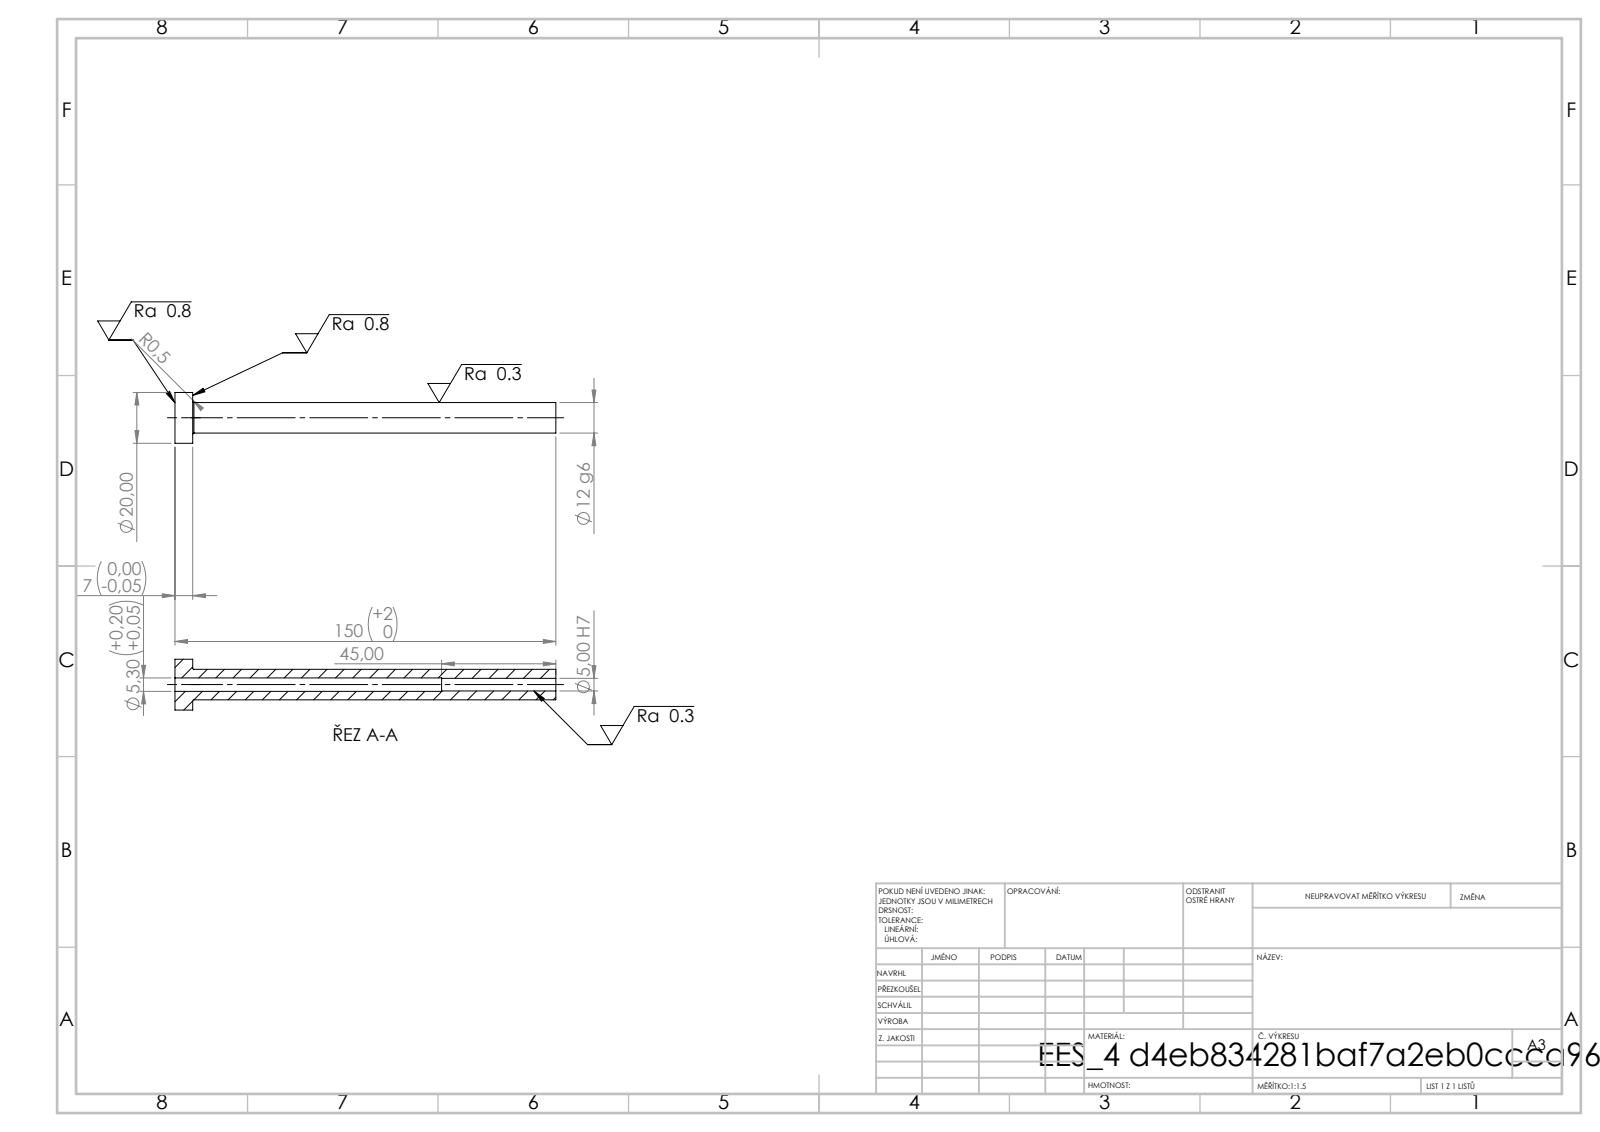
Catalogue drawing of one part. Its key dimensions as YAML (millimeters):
step_written_by: "SolidWorks 2019 (CONFIG_CONTROL_DESIGN)"
units: millimeters
bodies: {solids: 1, faces: 14, planar: 4, cylindrical: 8, other: 2}
overall_size: [150, 20, 20]
volume: 15174
surface_area: 8867
round_holes:
  - {diameter: 5, count: 1}
  - {diameter: 5.3, count: 1}
round_bosses_or_shafts:
  - {diameter: 20, count: 1}
  - {diameter: 12, count: 1}
face_to_face_distances: [7, 150, 143, 105, 98, 45]
